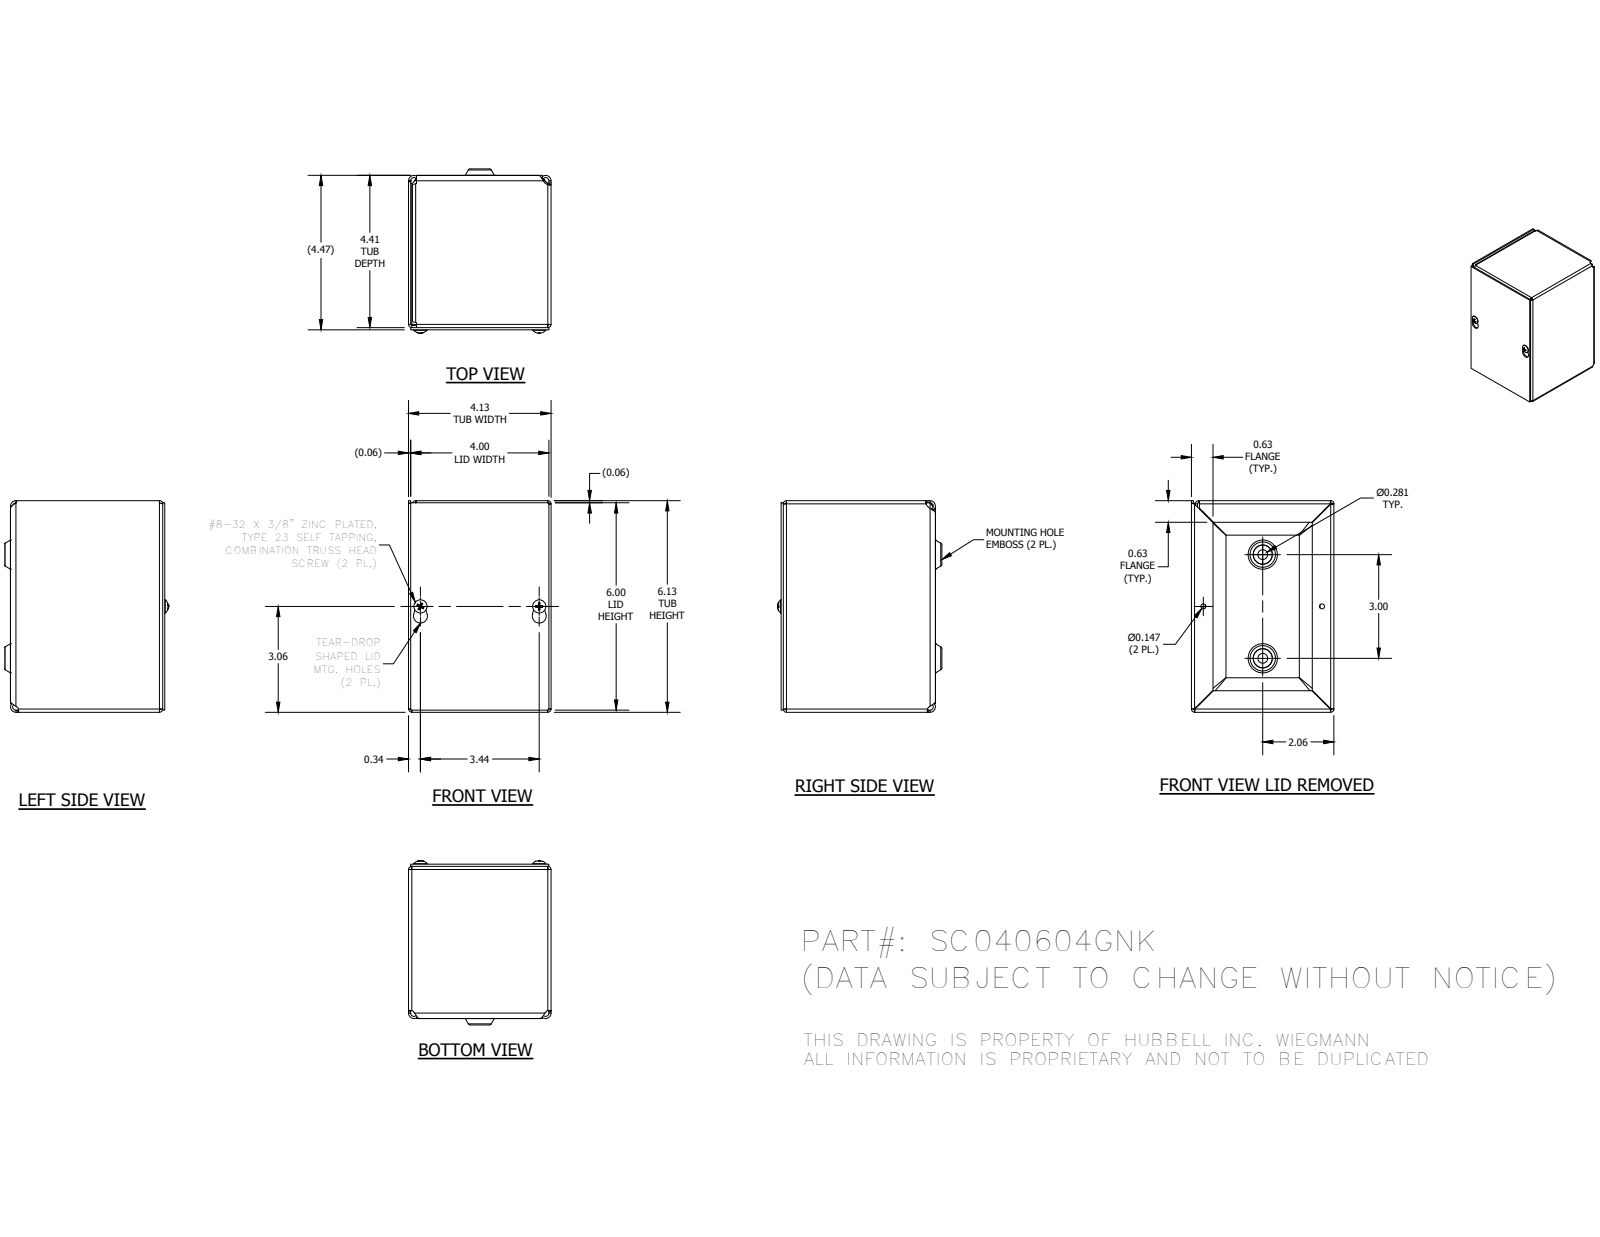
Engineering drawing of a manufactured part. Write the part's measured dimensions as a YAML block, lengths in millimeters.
part_name: "SC0406GNKBKP; SC040604GNKWRA; SC0406GNKLID; 34056 (+1 more)"
step_written_by: "Autodesk Inventor 2014 (AUTOMOTIVE_DESIGN)"
units: millimeters
bodies: {solids: 5, faces: 283, planar: 112, cylindrical: 59, other: 112}
overall_size: [155.57, 120.78, 104.78]
volume: 161560
surface_area: 209070
round_holes:
  - {diameter: 3.73, count: 2}
  - {diameter: 7.14, count: 2}
round_bosses_or_shafts:
  - {diameter: 9.75, count: 2}
  - {diameter: 4.17, count: 2}
partial_cylinders:
  - {radius: 0.79, count: 8}
  - {radius: 2.37, count: 8}
  - {radius: 1.4, count: 4}
  - {radius: 1.57, count: 4}
  - {radius: 2.38, count: 4}
  - {radius: 2.97, count: 4}
  - {radius: 3.15, count: 4}
  - {radius: 3.96, count: 4}
face_to_face_distances: [1.57, 1.58, 110.32, 103.2, 101.63, 104.78, 103.21, 111.89, 1.59, 111.91]
hole_center_spacings: [57.93, 57.95, 57.96, 76.2, 87.31]
